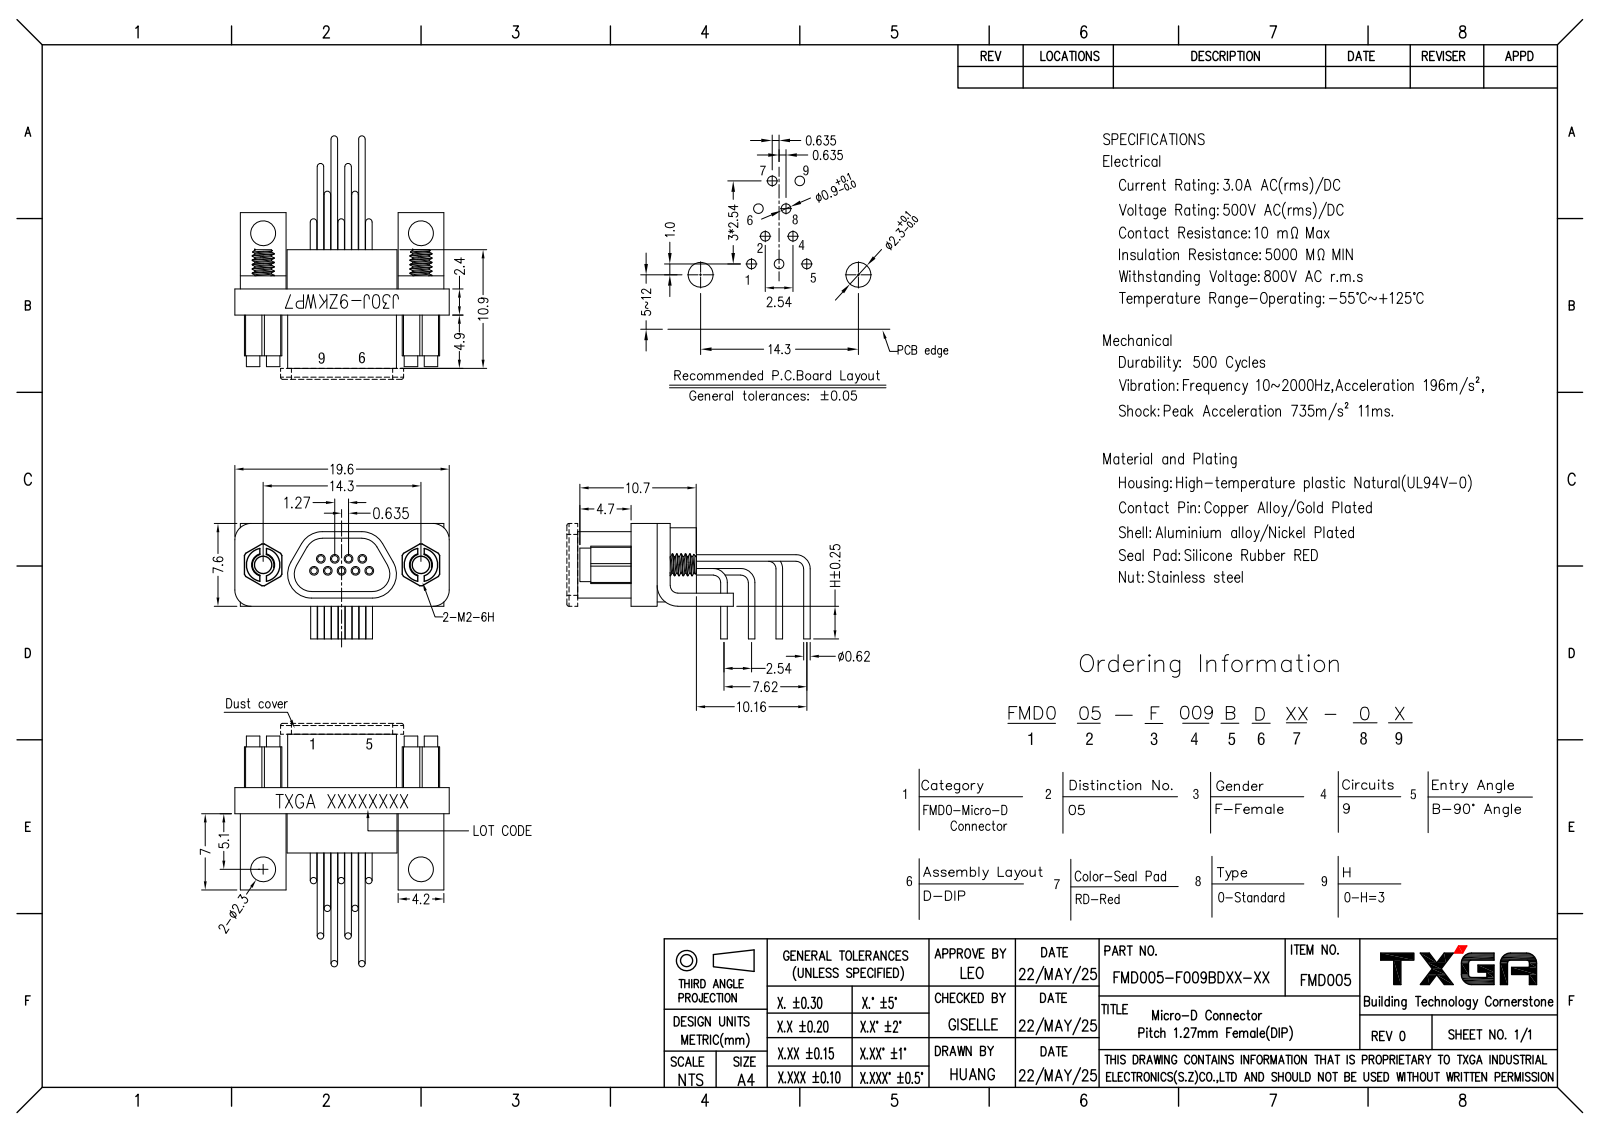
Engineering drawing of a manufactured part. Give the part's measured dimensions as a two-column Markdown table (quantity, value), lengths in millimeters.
| quantity | value |
| --- | --- |
| part name | FMD005-F009BDRD-00 |
| STEP written by | SolidWorks 2021 (CONFIG_CONTROL_DESIGN) |
| units | millimeters |
| bodies | 1 solid, 1089 faces (540 planar, 218 cylindrical, 331 other) |
| overall size | 21.37 × 19.6 × 10.62 |
| volume | 910 mm³ |
| surface area | 1 551 mm² |
| round holes (diameter × count) | 0.6 × 9, 1.6 × 2, 1.8 × 2, 2.3 × 2 |
| round bosses / shafts (diameter × count) | 0.62 × 18, 0.8 × 9, 3.1 × 2, 2 × 2 |
| partial cylindrical surfaces (radius × count) | 0.3 × 12, 1.5 × 4, 1.7 × 4, 2 × 4, 2.4 × 4, 1.15 × 2, 0.7 × 1, 1.9 × 1 |
| main face-to-face distances | 3.6, 2.4, 1.2, 6, 0.7, 14.3, 0.36, 7.2, 0.4, 0.75 |
| hole center spacings | 1.27, 2.2, 2.54, 3.36, 3.81, 1.26, 1.28, 4.58 |
